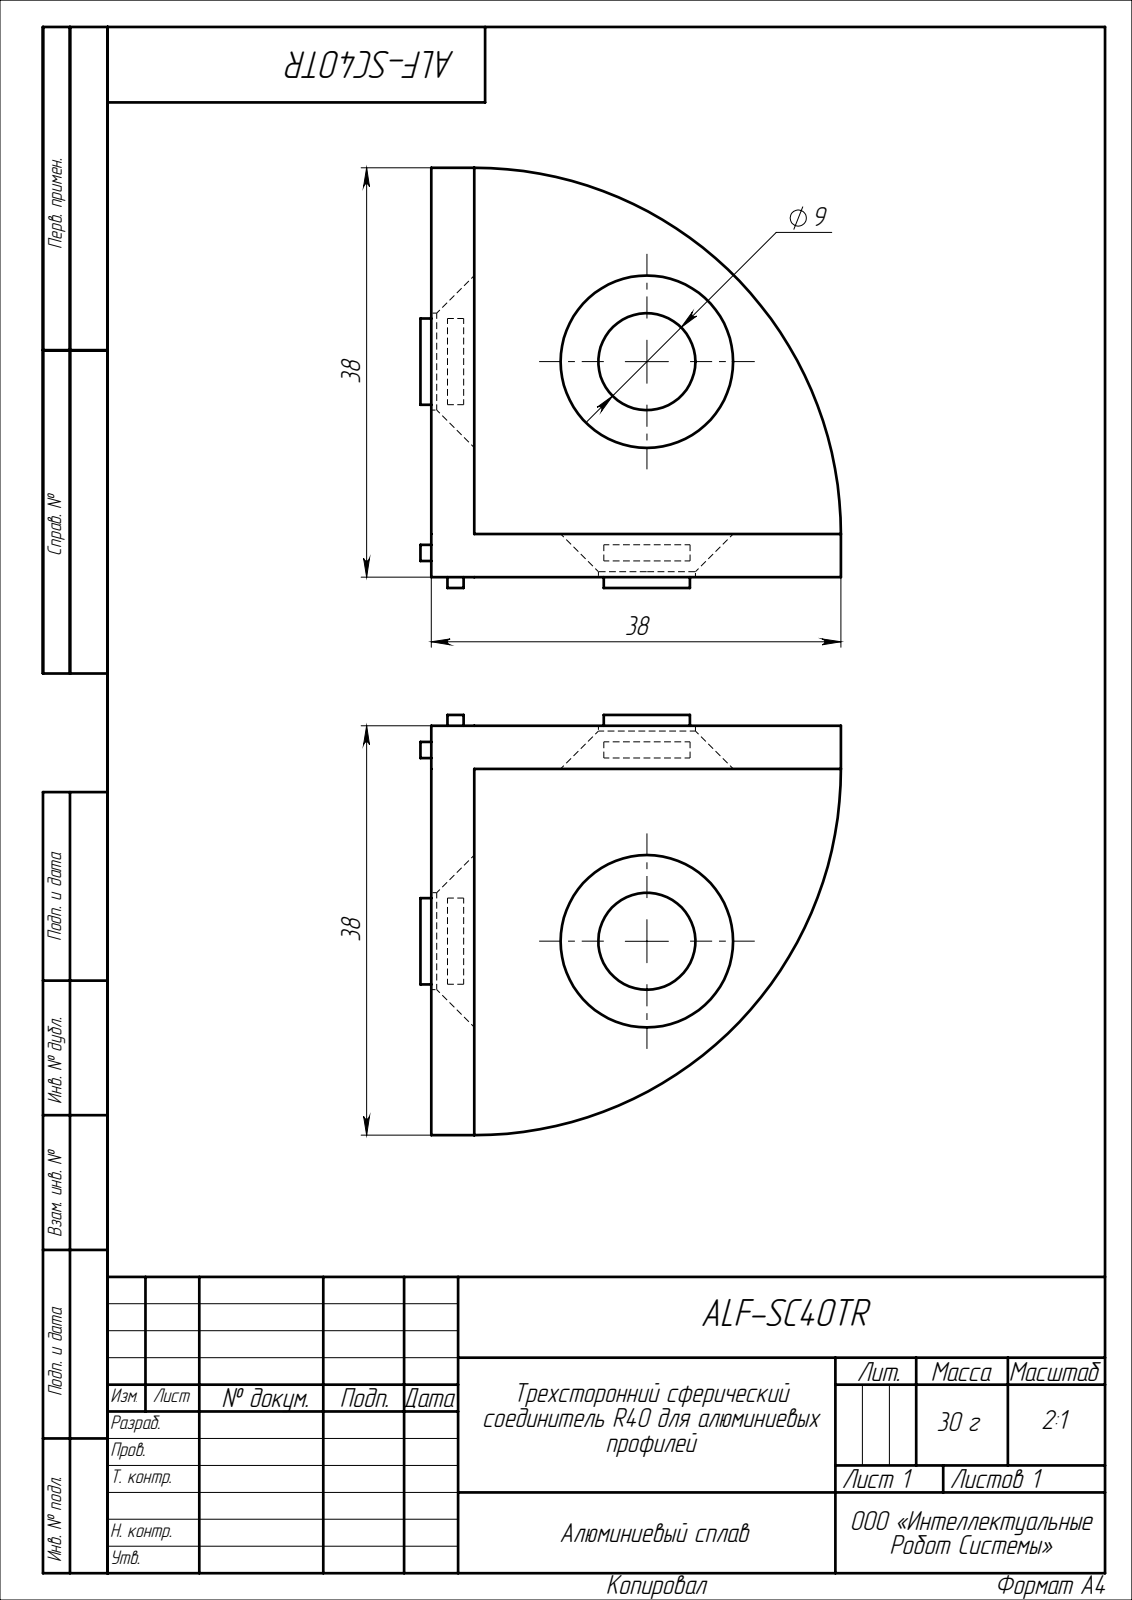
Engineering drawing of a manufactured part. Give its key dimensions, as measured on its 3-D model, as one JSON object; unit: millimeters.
{"part_name": "ALF-SC40TR", "step_written_by": "SolidWorks 2022 (CONFIG_CONTROL_DESIGN)", "units": "millimeters", "bodies": {"solids": 1, "faces": 66, "planar": 52, "cylindrical": 14, "other": 0}, "overall_size": [41.5, 41.5, 20], "volume_mm3": 21326, "surface_area_mm2": 9040, "round_holes": [[8, 2], [13, 2]], "face_to_face_distances": [20, 40, 15.5, 4.5, 11, 26, 14, 37, 3, 1.5]}
